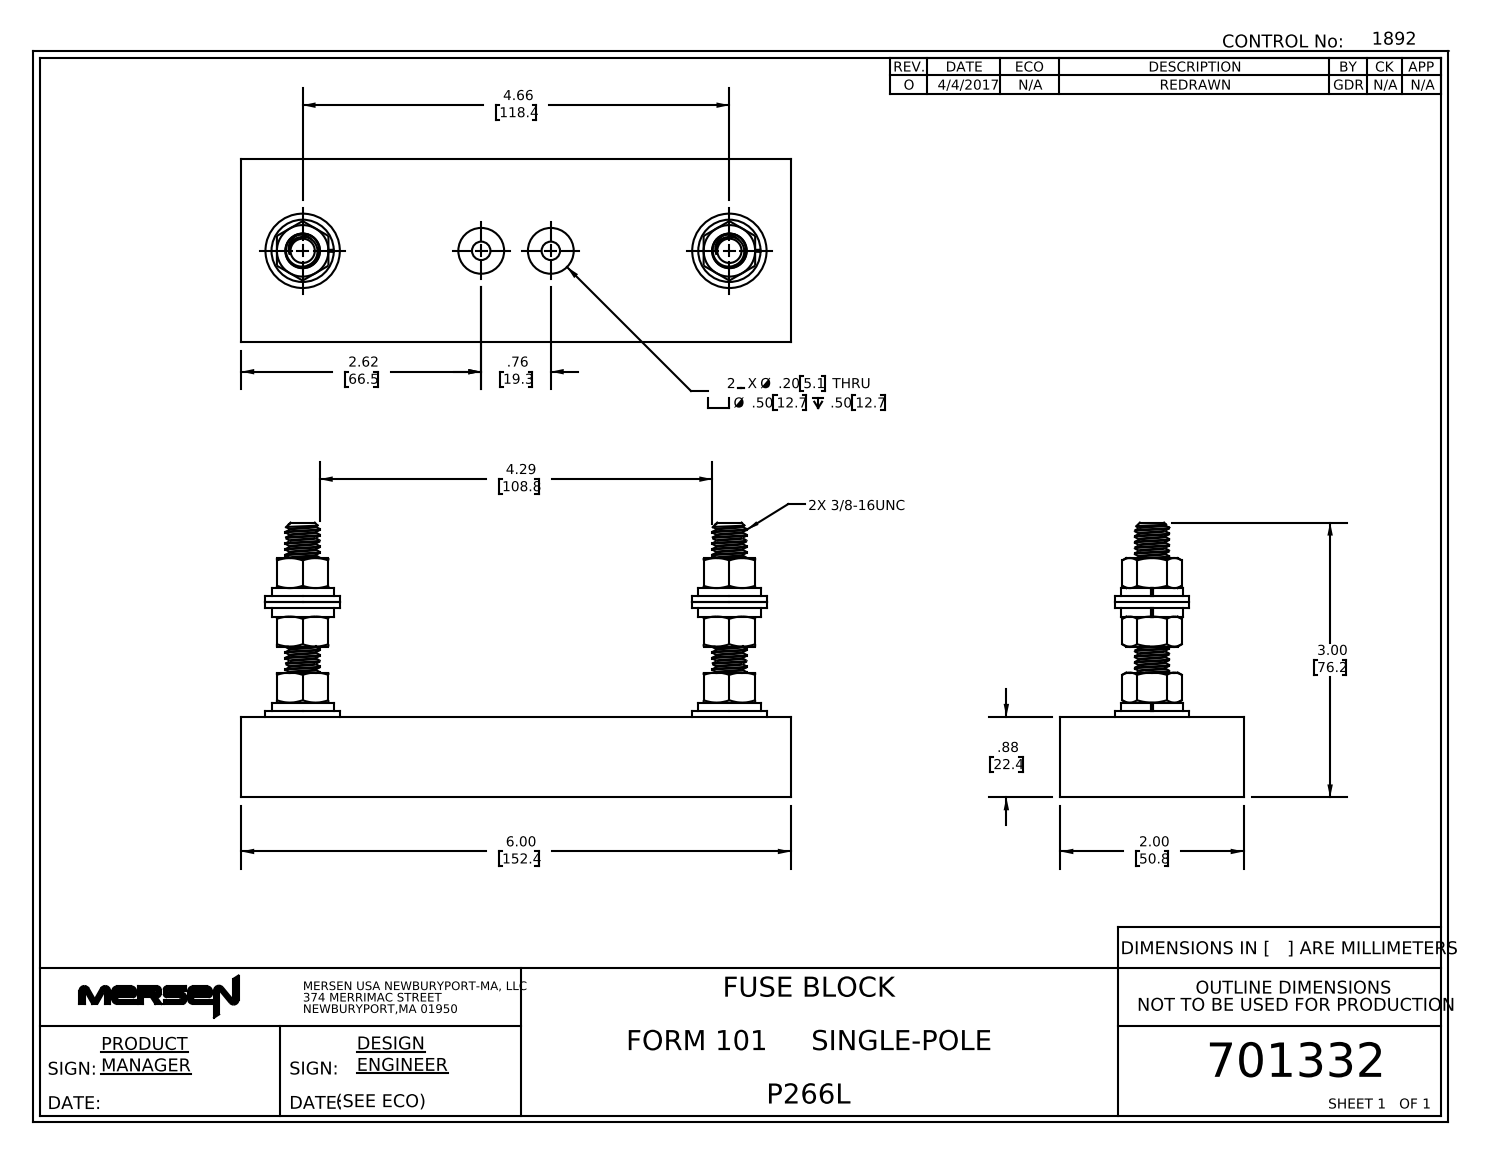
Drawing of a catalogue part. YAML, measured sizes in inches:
part_name: "701332revO"
step_written_by: "SolidWorks 2016 (AUTOMOTIVE_DESIGN)"
units: inches
bodies: {solids: 0, faces: 152, planar: 78, cylindrical: 18, other: 56}
overall_size: [6, 3, 2]
round_holes:
  - {diameter: 0.201, count: 2}
  - {diameter: 0.5, count: 2}
round_bosses_or_shafts:
  - {diameter: 0.812, count: 2}
  - {diameter: 0.68, count: 2}
  - {diameter: 0.375, count: 2}
face_to_face_distances: [0.88, 2, 1.25, 0.065, 6, 2.13, 1.185, 0.155, 0.09, 1.095]
hole_center_spacings: [0.76]
